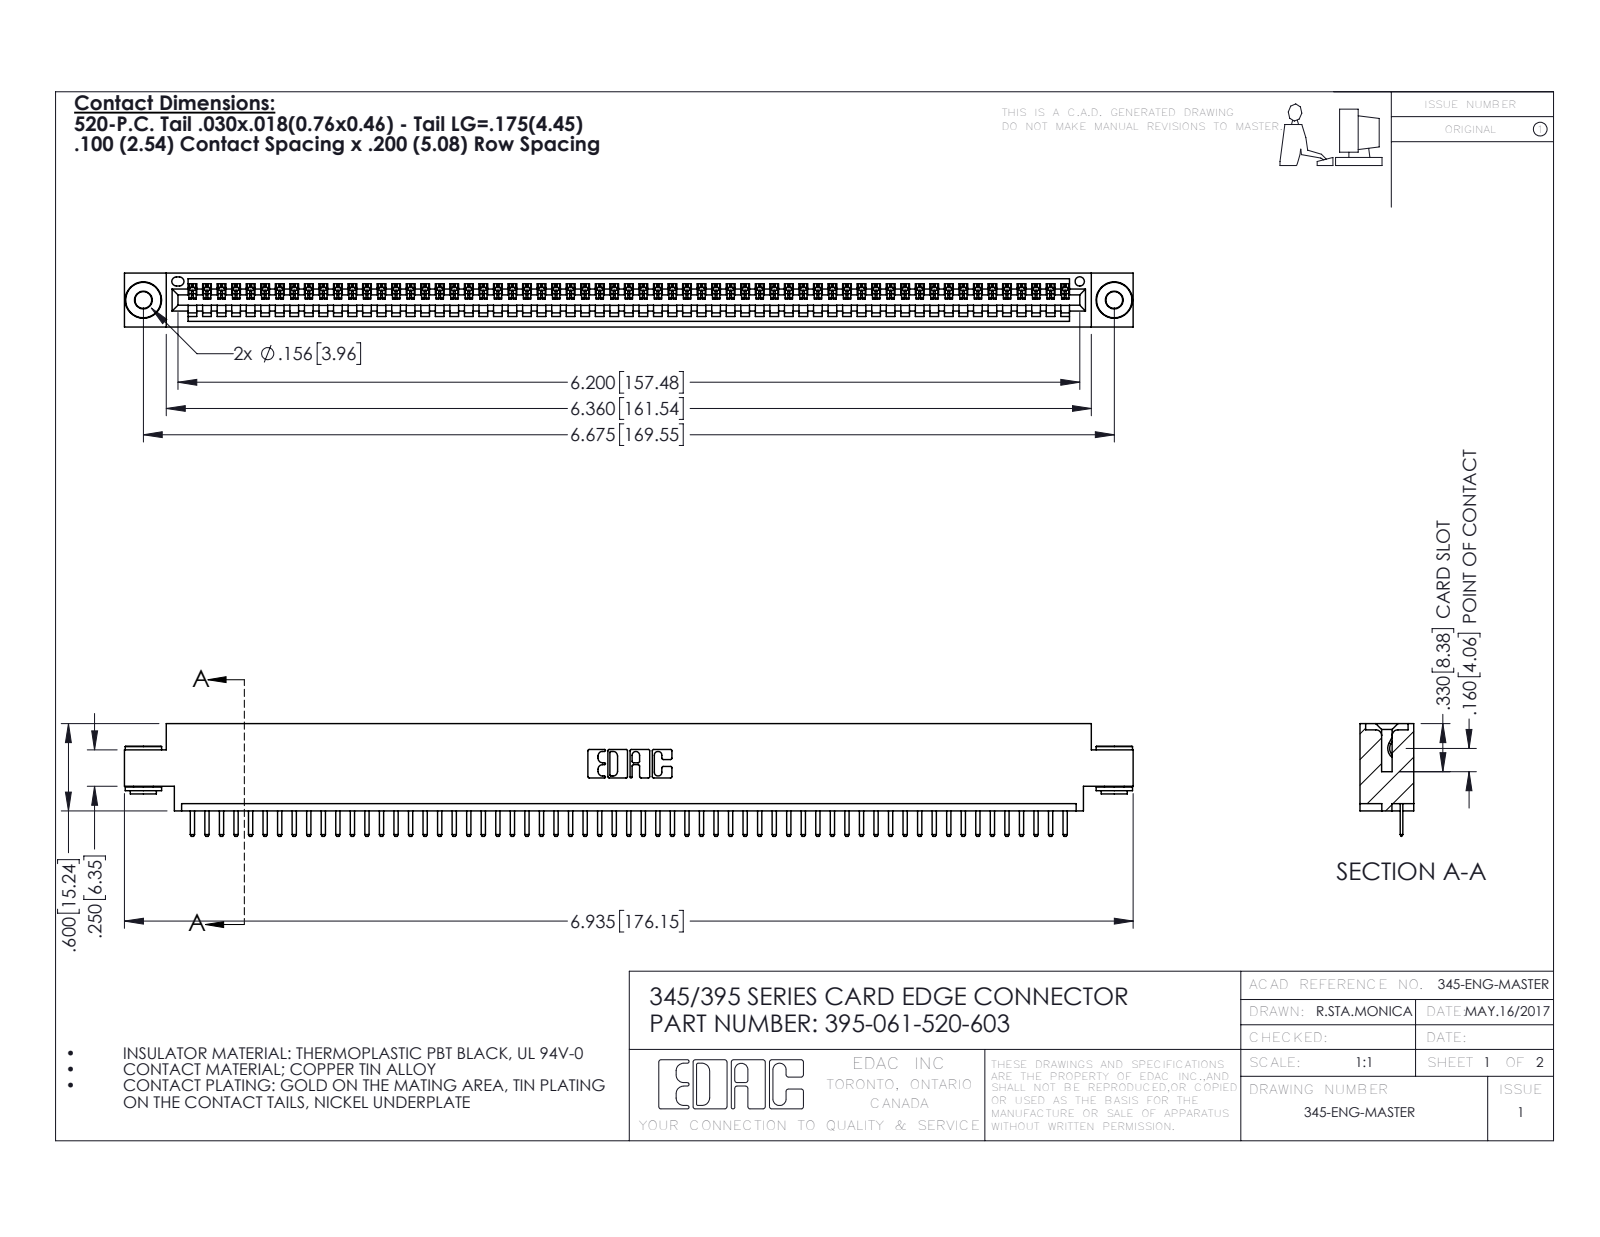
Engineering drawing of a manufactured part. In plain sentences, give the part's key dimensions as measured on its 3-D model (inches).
The part is named "395-061-520-603; 345-250-002_345-250-002-102; 345 Part_0.170 Offset - 0.156 Dia-TH; 345-292-001_345-293-120". Its 3-D file was written by "SolidWorks 2016 (CONFIG_CONTROL_DESIGN)". It is 64 solids with 3950 faces: 2656 planar, 1286 cylindrical and 8 other. Overall it measures 6.935 by 0.775 by 0.37 inches. Its volume is 1.014 cubic inches and its surface area 34.27 square inches. Round holes: 2 of diameter 0.116, 2 of diameter 0.156, 1 of diameter 0.064. Round bosses or shafts: 2 of diameter 0.25, 2 of diameter 0.18, 2 of diameter 0.136. Partial cylindrical surfaces (rounded edges, fillets, slot ends): 124 of radius 0.01, 122 of radius 0.006, 22 of radius 0.01, 6 of radius 0.007, 6 of radius 0.031, 3 of radius 0.026, 2 of radius 0.031, 2 of radius 0.04. The main face-to-face distances are 0.072, 0.298, 0.37, 0.2, 0.098, 0.272, 0.025, 0.225, 0.072, 0.175. The hole center spacings are 0.27, 6.439, 6.675.
